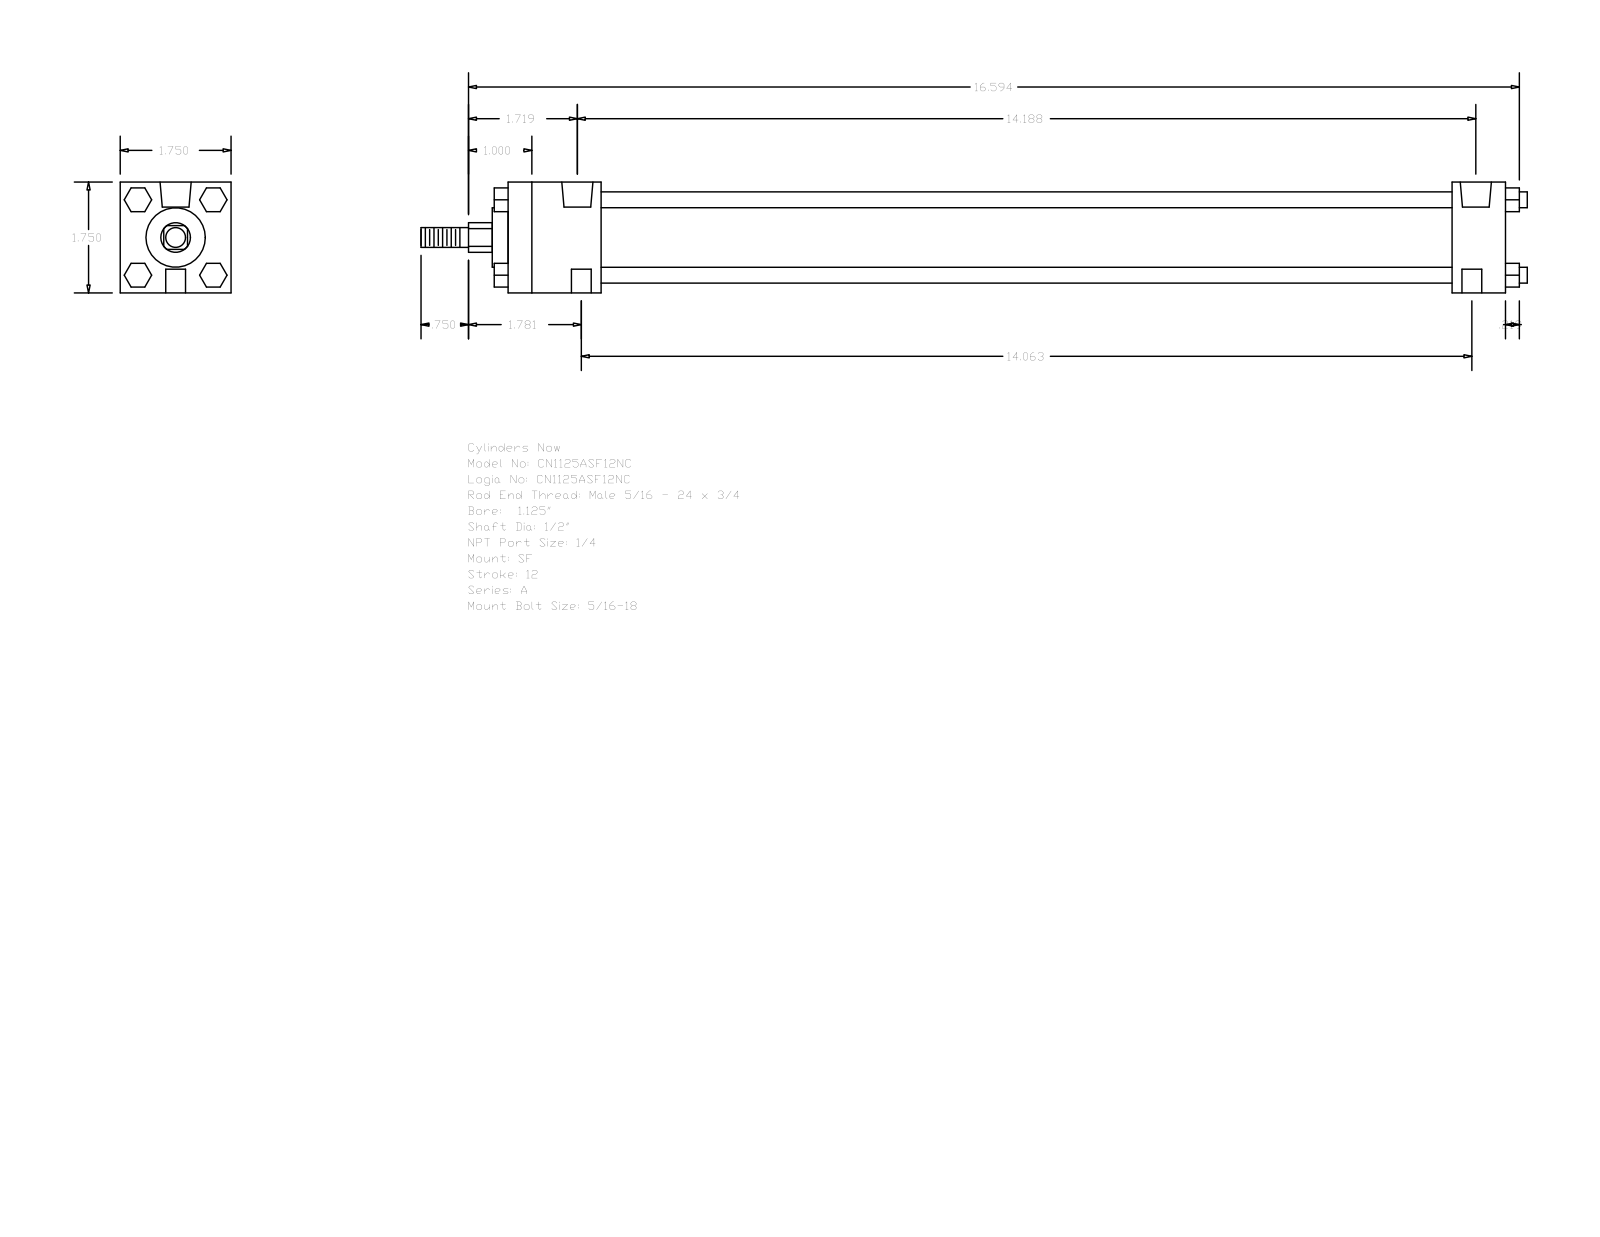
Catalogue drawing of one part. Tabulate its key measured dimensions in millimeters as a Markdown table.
| quantity | value |
| --- | --- |
| part name | A_SF__0112_0.5 |
| STEP written by | GSSL Pune (CONFIG_CONTROL_DESIGN) |
| units | millimeters |
| bodies | 0 solids, 120 faces (92 planar, 28 cylindrical, 0 other) |
| overall size | 443.71 × 44.45 × 44.45 |
| round holes (diameter × count) | 5.56 × 2, 7.94 × 2, 12.49 × 2 |
| round bosses / shafts (diameter × count) | 6.35 × 4, 31.88 × 1, 23.81 × 1, 12.7 × 1, 7.94 × 1 |
| partial cylindrical surfaces (radius × count) | 5.94 × 1 |
| main face-to-face distances | 44.46, 400.05, 378.61, 21.44, 37.3, 341.31, 362.75, 9.53, 5.59, 26.99 |
| hole center spacings | 357.19, 1.58, 1.59, 358.77, 358.78, 360.36 |
